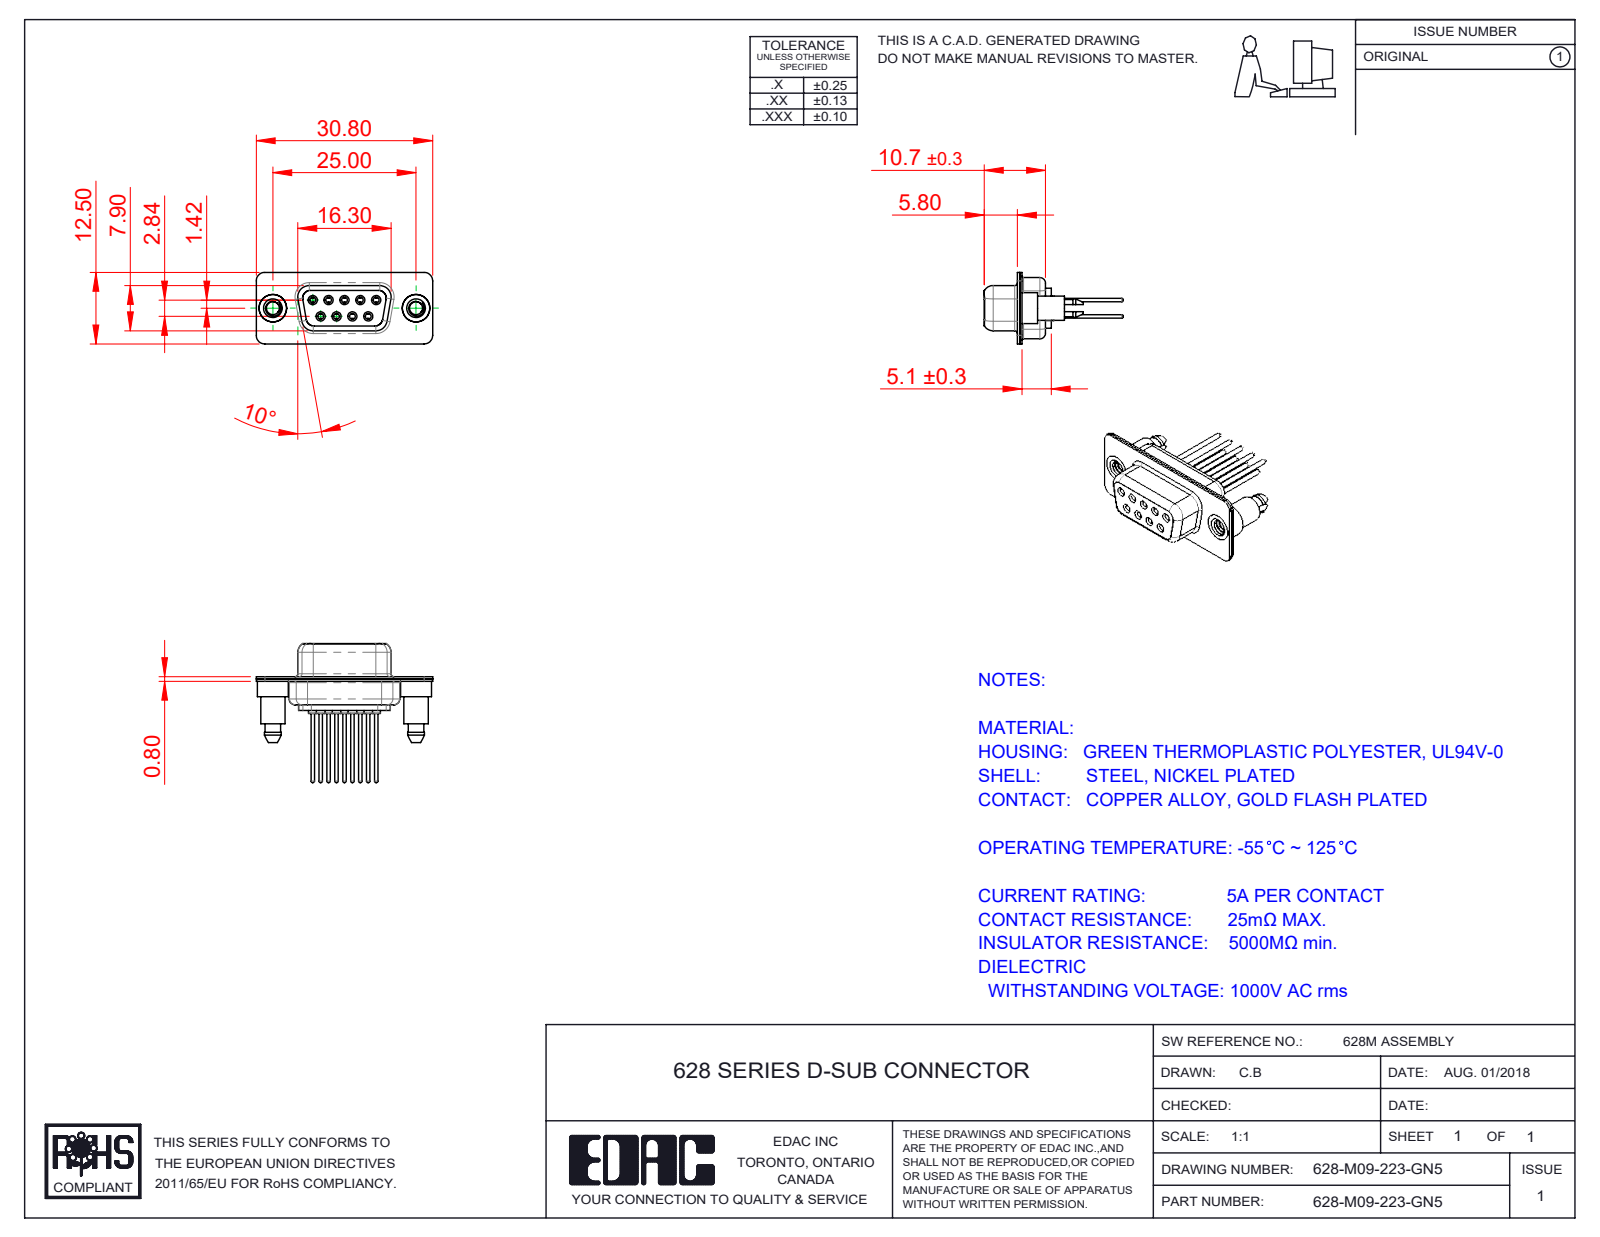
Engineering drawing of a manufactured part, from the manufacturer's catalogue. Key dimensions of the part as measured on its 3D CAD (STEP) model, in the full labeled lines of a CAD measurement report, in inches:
Part name (STEP PRODUCT): 628M Shell Front_09 Contacts; 628M Contact Row 2_23; 628M Housing_09 Contacts; 628M 4-40 Threaded Boardlock (+3 more)
STEP written by: SolidWorks 2020 (CONFIG_CONTROL_DESIGN)
Units: inches
Bodies: 14 solids, 824 faces (218 planar, 340 cylindrical, 266 other)
Overall size (bounding box): 1.213 × 0.956 × 0.492
Volume: 0.113 in³ · Surface area: 7.547 in²
Round holes (diameter × count): ⌀0.039 ×9, ⌀0.043 ×9, ⌀0.067 ×9, ⌀0.071 ×9, ⌀0.079 ×9, ⌀0.089 ×2, ⌀0.157 ×2, ⌀0.189 ×2
Round bosses / shafts (diameter × count): ⌀0.087 ×9, ⌀0.063 ×9, ⌀0.059 ×9, ⌀0.024 ×9, ⌀0.213 ×2, ⌀0.193 ×2, ⌀0.167 ×2
Partial cylindrical surfaces — rounded edges, fillets, slot ends (radius × count): R0.059 ×18, R0.079 ×12, R0.063 ×10, R0.053 ×8, R0.01 ×4, R0.02 ×4, R0.024 ×4, R0.026 ×4
Main face-to-face distances: 0.016, 0.055, 0.018, 0.333, 0.031, 0.071, 0.039, 0.35, 0.244, 0.278
Hole centre spacings: 0.124, 0.109, 0.218, 0.198, 0.198, 0.327, 0.28, 0.294
